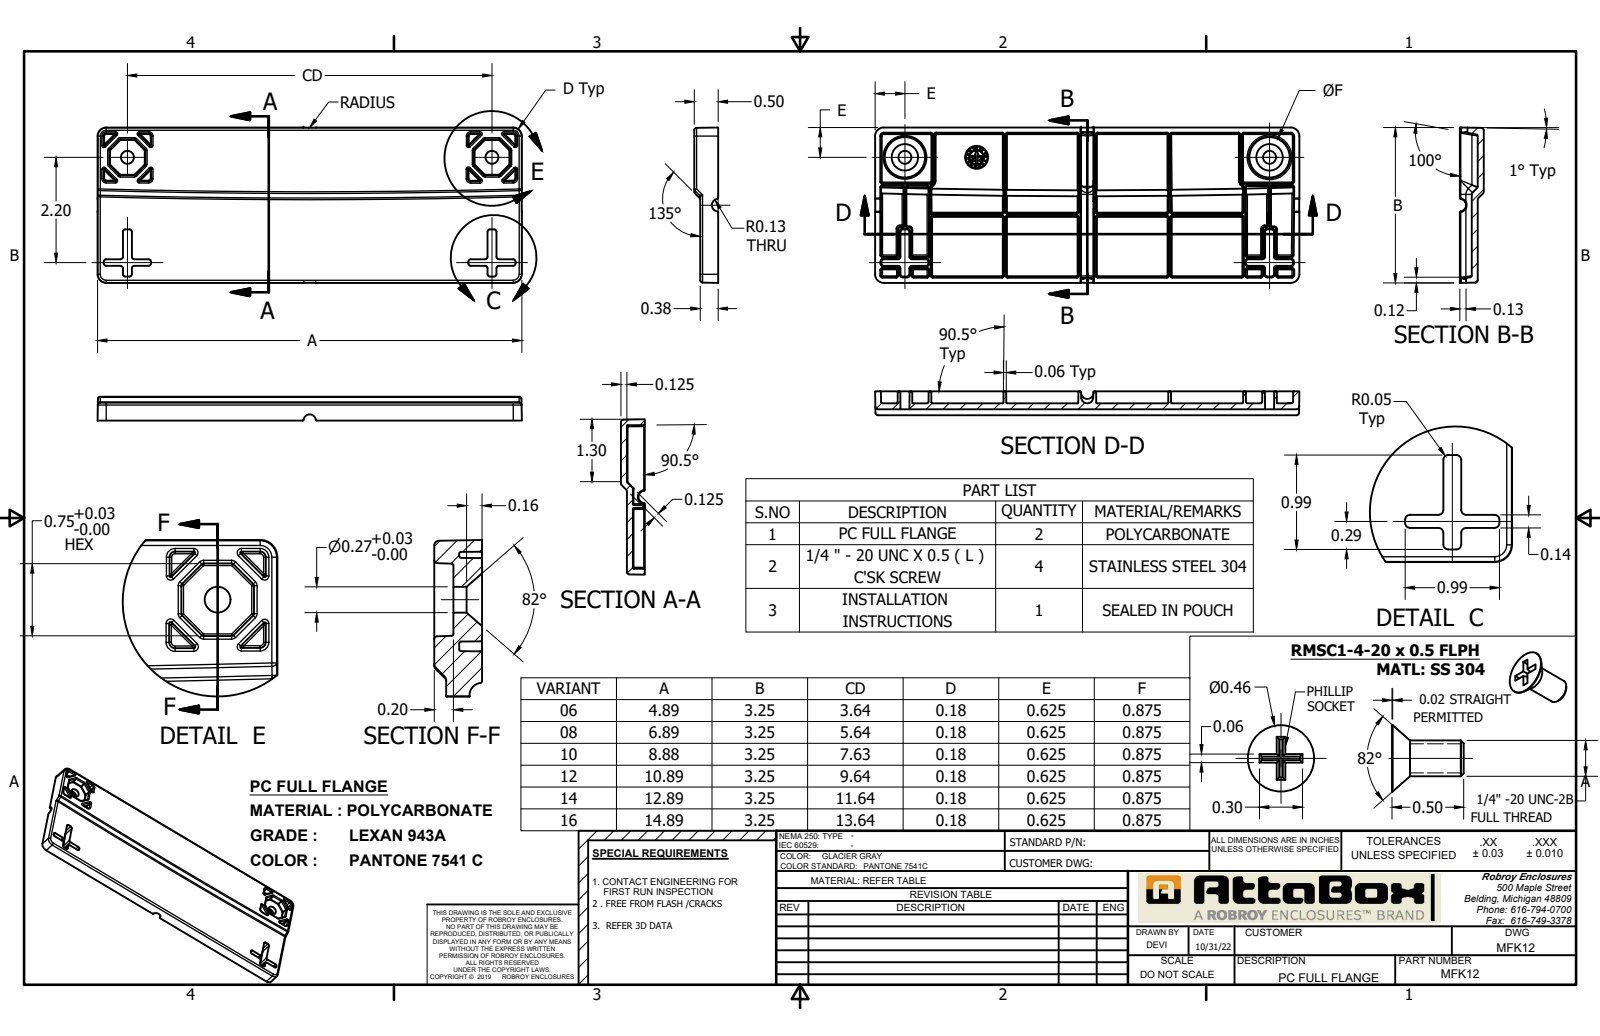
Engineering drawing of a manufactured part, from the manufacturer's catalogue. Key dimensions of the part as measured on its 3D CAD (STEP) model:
Part name (STEP PRODUCT): MFK12_Default
STEP written by: SolidWorks 2023 (CONFIG_CONTROL_DESIGN)
Units: inches
Bodies: 1 solid, 1195 faces (334 planar, 397 cylindrical, 464 other)
Overall size (bounding box): 10.89 × 3.25 × 0.5
Volume: 6.291 in³ · Surface area: 110.7 in²
Round holes (diameter × count): ⌀0.27 ×2
Partial cylindrical surfaces — rounded edges, fillets, slot ends (radius × count): R0.02 ×122, R0.03 ×117, R0.05 ×6, R0.125 ×3, R0.12 ×1, R0.129 ×1, R0.129 ×1, R0.13 ×1
Main face-to-face distances: 0.25, 0.125, 0.125, 0.5, 0.375, 1.33, 1.731, 2.069, 4.454, 2.385
Hole centre spacings: 9.64
